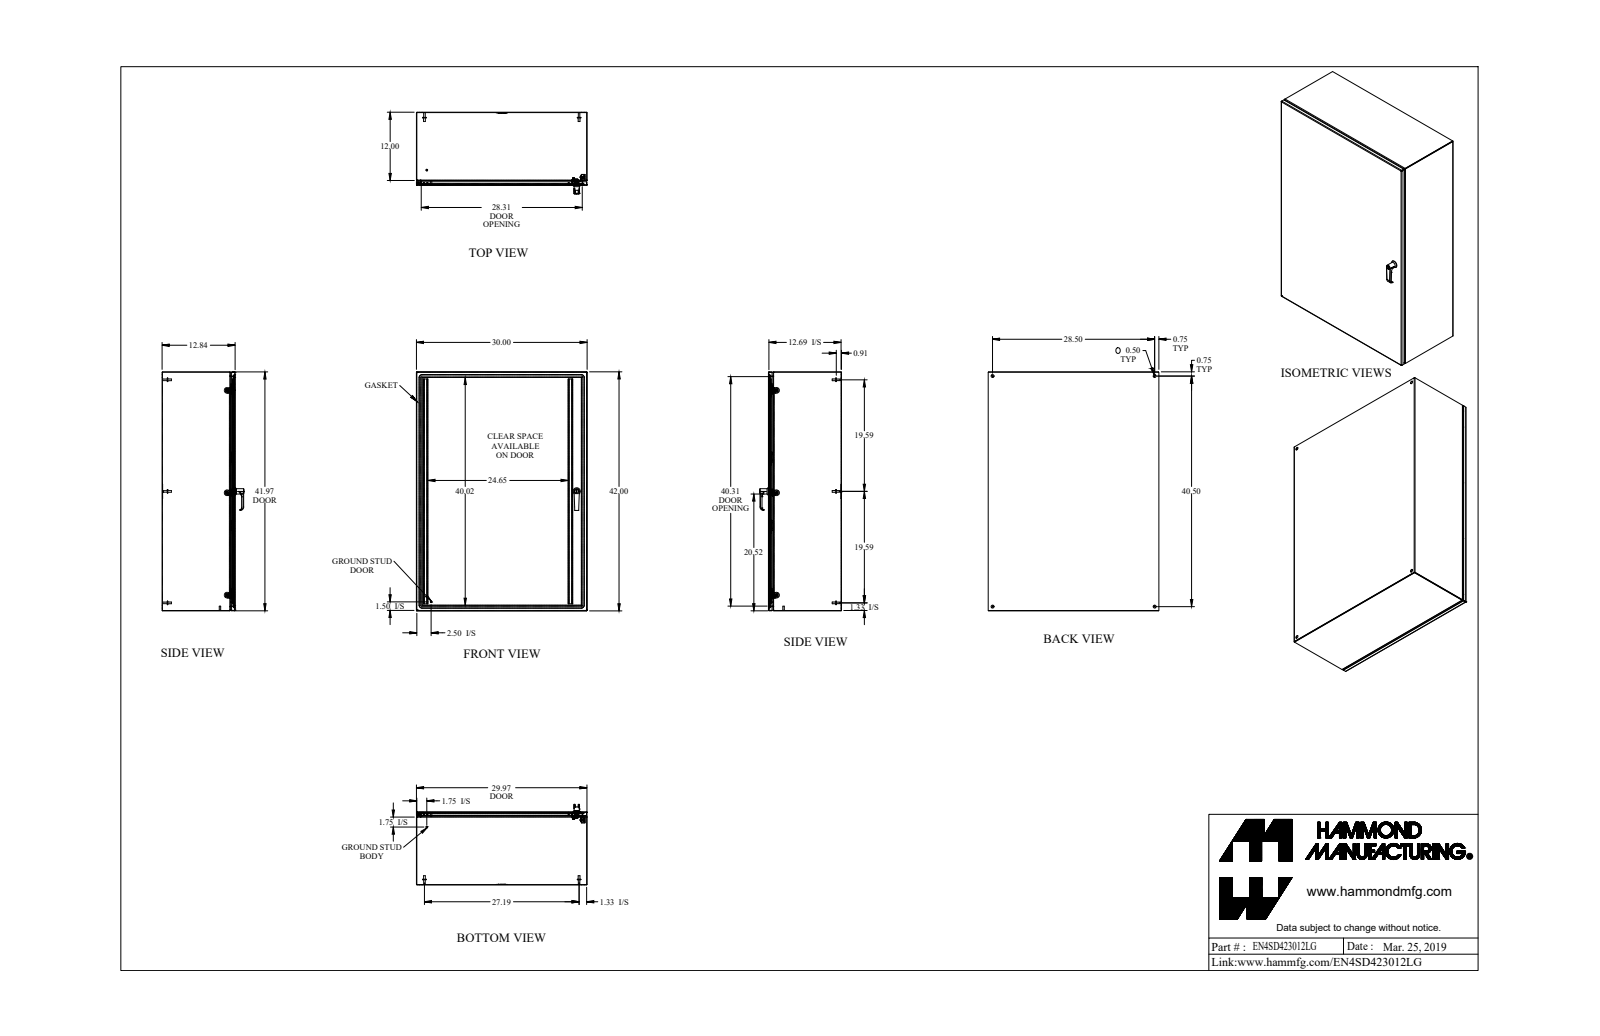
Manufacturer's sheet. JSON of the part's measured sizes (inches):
{"part_name": "EN4SD423012LG", "step_written_by": "SolidWorks 2019 (AUTOMOTIVE_DESIGN)", "units": "inches", "bodies": {"solids": 55, "faces": 1443, "planar": 632, "cylindrical": 532, "other": 279}, "overall_size": [42, 30, 14.367], "volume_in3": 354, "surface_area_in2": 9825, "round_holes": [[0.176, 6], [0.5, 4], [0.196, 3], [0.25, 3], [0.265, 3], [0.413, 3], [0.256, 2], [0.313, 2], [0.394, 2], [0.172, 1], [0.24, 1], [0.242, 1]], "round_bosses_or_shafts": [[0.25, 7], [0.625, 6], [0.375, 6], [0.313, 6], [0.27, 6], [0.156, 6], [1, 3], [0.63, 2]], "partial_cylinders_radius": [[0.036, 18], [0.108, 18], [0.03, 15], [0.043, 12], [0.081, 12], [0.006, 8], [0.048, 8], [0.062, 8]], "face_to_face_distances": [0.072, 12.765, 12.693, 12.837, 29.928, 41.928, 29.856, 30, 41.856, 42], "hole_center_spacings": [0.787, 2.507, 17.981, 17.988, 18, 27.52, 28.5, 35.969]}
